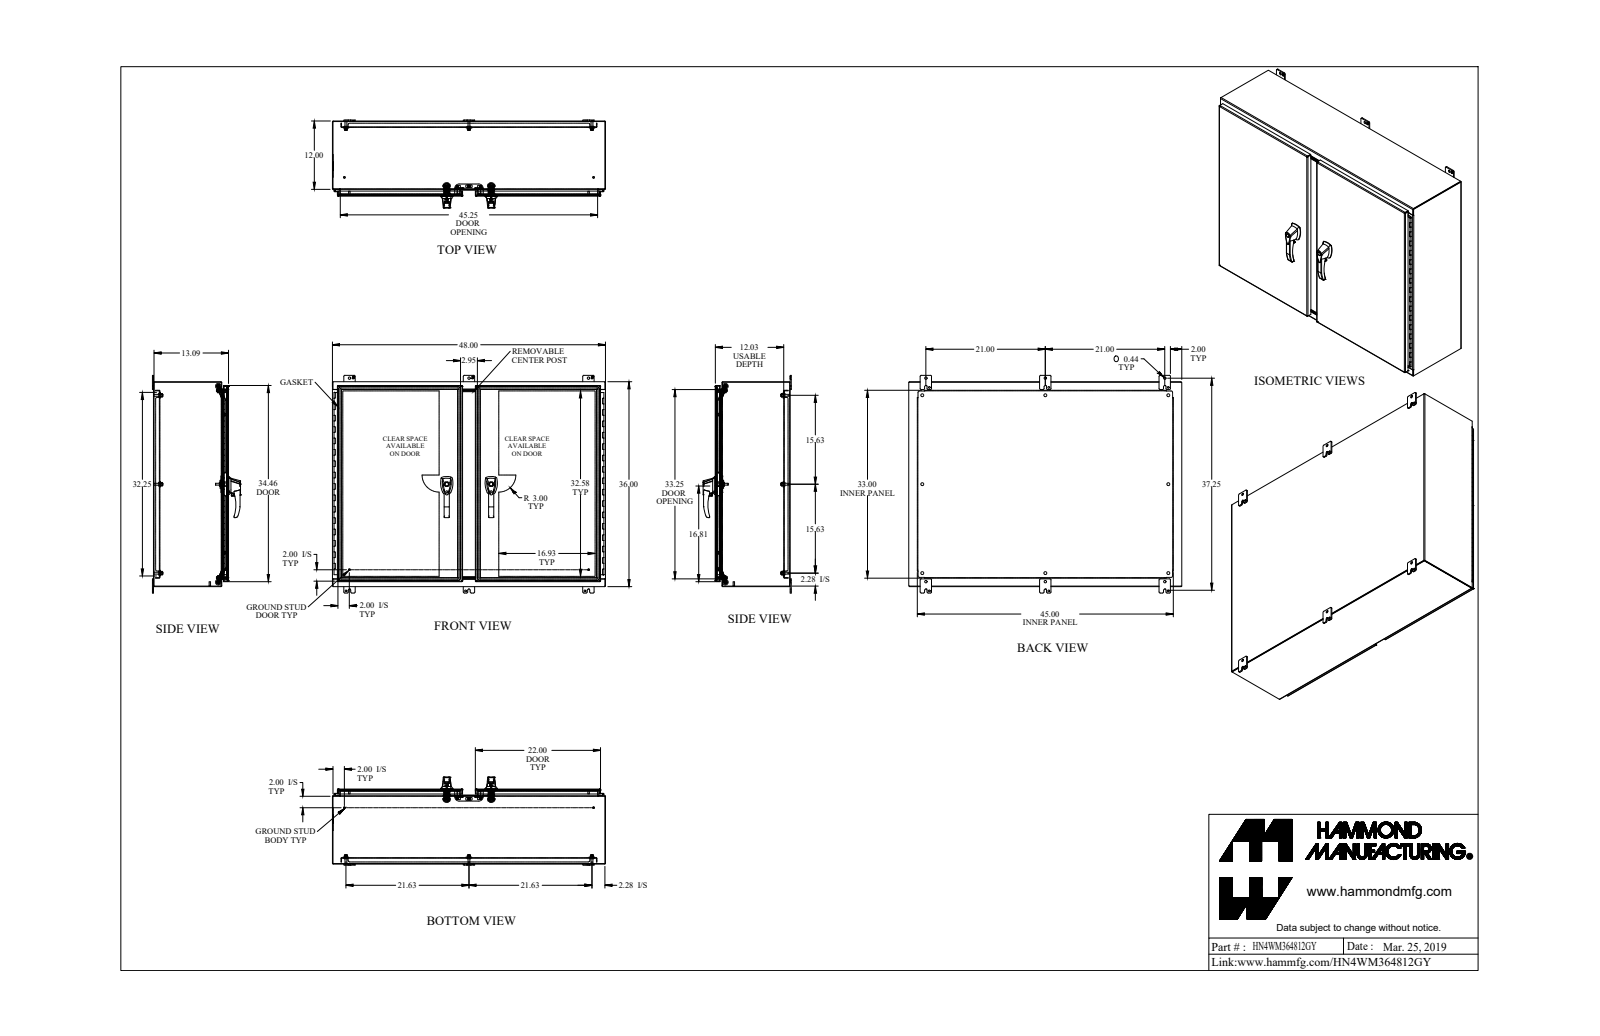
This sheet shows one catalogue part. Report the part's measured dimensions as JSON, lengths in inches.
{"part_name": "HN4WM364812GY", "step_written_by": "SolidWorks 2018 (AUTOMOTIVE_DESIGN)", "units": "inches", "bodies": {"solids": 110, "faces": 2952, "planar": 1387, "cylindrical": 1281, "other": 284}, "overall_size": [48, 38.25, 15.487], "volume_in3": 806.7, "surface_area_in2": 16733, "round_holes": [[0.304, 12], [0.307, 8], [0.5, 8], [0.313, 6], [0.445, 6], [0.25, 5], [0.281, 4], [0.313, 4], [0.39, 4], [0.201, 3], [0.437, 3], [0.11, 2]], "round_bosses_or_shafts": [[1, 10], [0.65, 8], [0.375, 8], [0.33, 8], [0.281, 8], [0.75, 4], [0.625, 4], [0.44, 4]], "partial_cylinders_radius": [[0.125, 35], [0.25, 34], [0.018, 32], [0.188, 25], [0.06, 20], [0.048, 17], [0.143, 17], [0.5, 17]], "face_to_face_distances": [0.095, 1.032, 0.095, 13.09, 12.995, 0.937, 13.185, 13.09, 1.127, 11.963], "hole_center_spacings": [6, 46.53, 12, 47.677, 18, 46.142, 49.528, 15.625]}
